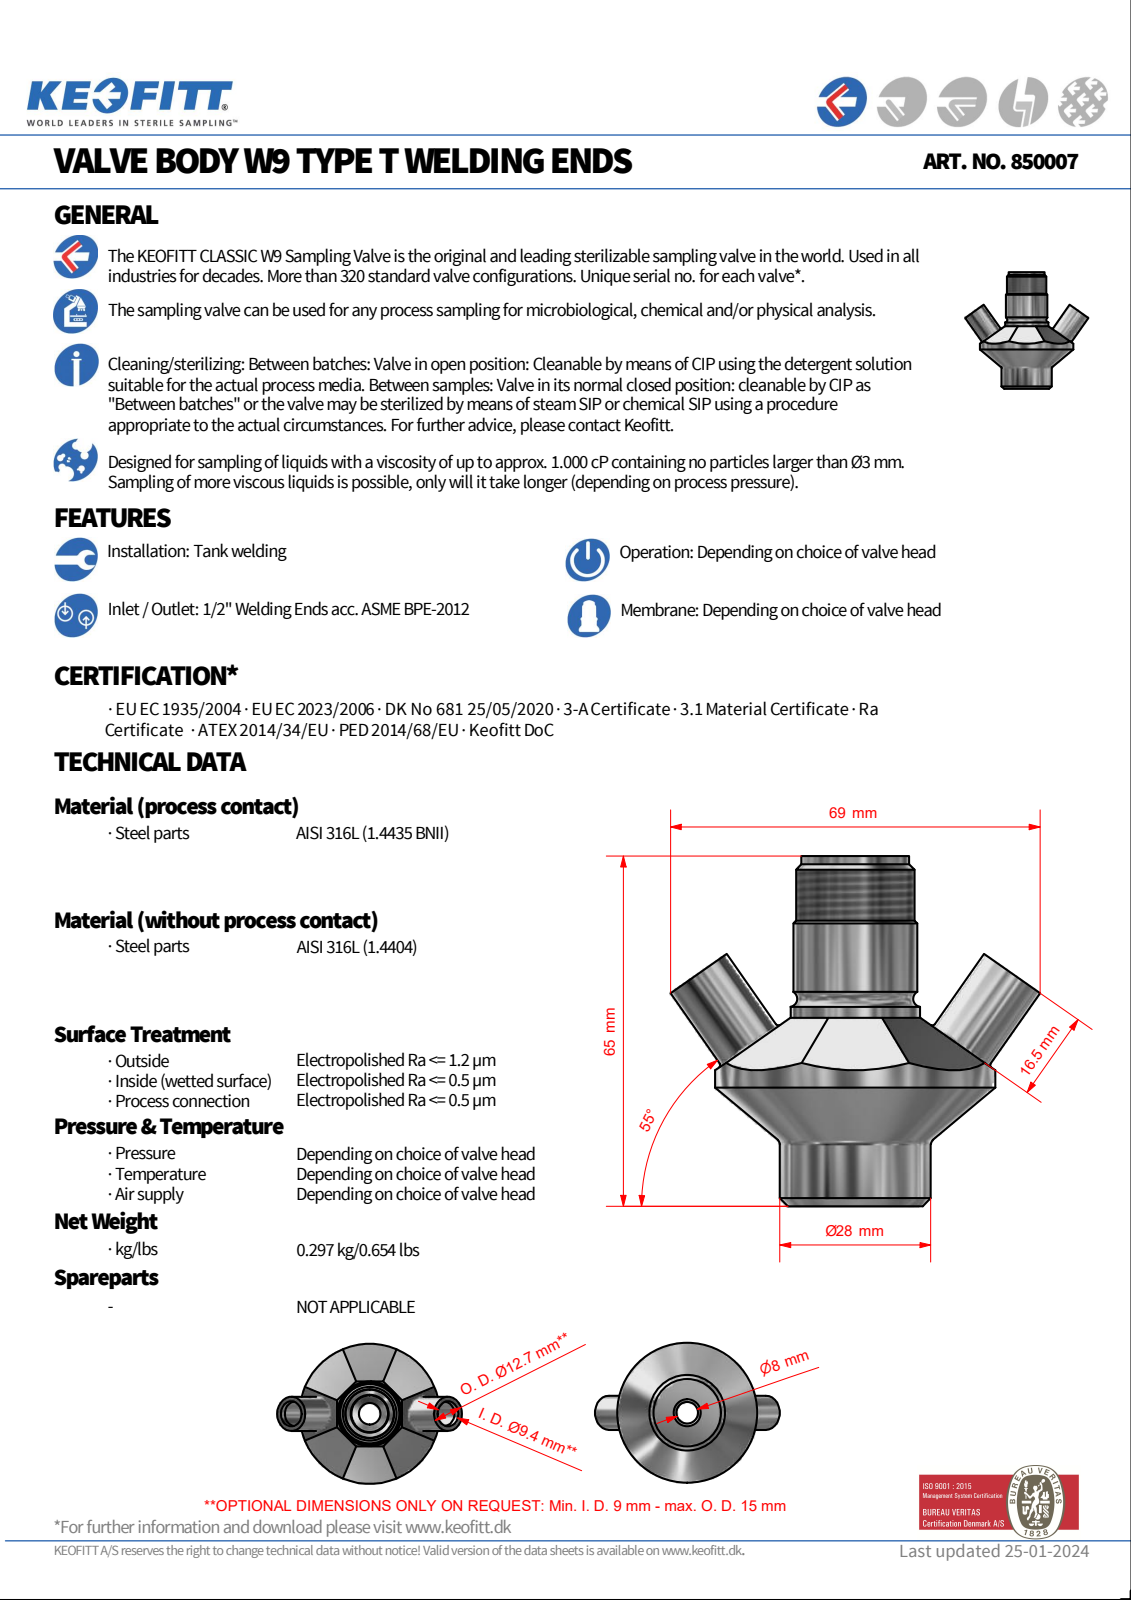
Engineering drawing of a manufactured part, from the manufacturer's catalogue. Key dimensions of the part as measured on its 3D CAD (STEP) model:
Part name (STEP PRODUCT): 850007
STEP written by: Autodesk Inventor 2020 (AUTOMOTIVE_DESIGN)
Units: millimetres
Bodies: 1 solid, 51 faces (19 planar, 19 cylindrical, 13 other)
Overall size (bounding box): 68.59 × 65 × 52
Volume: 48 691 mm³ · Surface area: 16 202 mm²
Round holes (diameter × count): ⌀9 ×2, ⌀18.1 ×1, ⌀21 ×1
Round bosses / shafts (diameter × count): ⌀12.7 ×2, ⌀52 ×1, ⌀28 ×1, ⌀24 ×1, ⌀23 ×1, ⌀22 ×1, ⌀20.5 ×1, ⌀20 ×1
Main face-to-face distances: 62.5, 16.5, 35, 27.5, 29.2, 5.8, 33.3, 65, 35.8, 30
